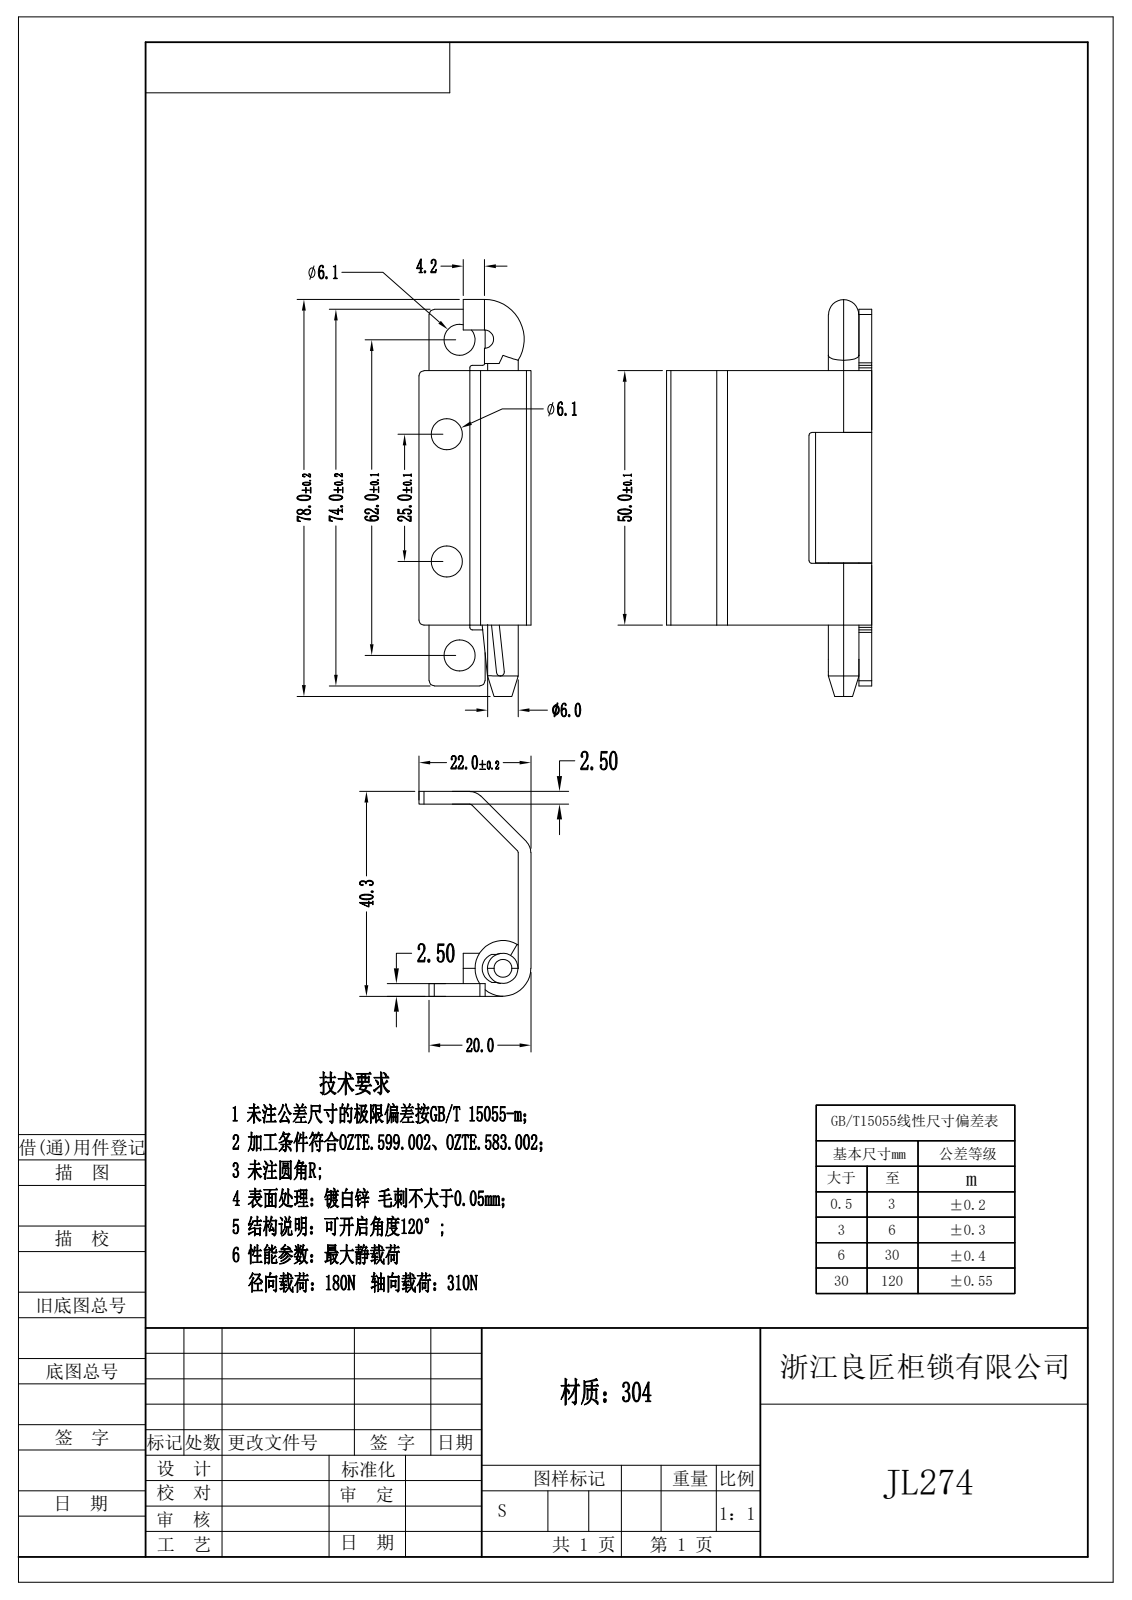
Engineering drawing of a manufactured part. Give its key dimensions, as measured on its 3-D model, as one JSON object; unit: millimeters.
{"step_written_by": "Rhino 8.5 (CONFIG_CONTROL_DESIGN)", "units": "millimeters", "bodies": {"solids": 6, "faces": 82, "planar": 43, "cylindrical": 31, "other": 8}, "overall_size": [76.41, 40.3, 22], "volume_mm3": 12118, "surface_area_mm2": 11392, "round_holes": [[6.1, 4], [5.99, 1]], "round_bosses_or_shafts": [[10.99, 1], [5.39, 1]], "partial_cylinders_radius": [[0.5, 6], [1, 6], [3, 2], [0.68, 1]], "face_to_face_distances": [2.5, 37.8, 40.3, 35.3, 12.25, 17.5, 20, 50, 2.49, 37.79], "hole_center_spacings": [18.67, 43.57, 25, 62]}
